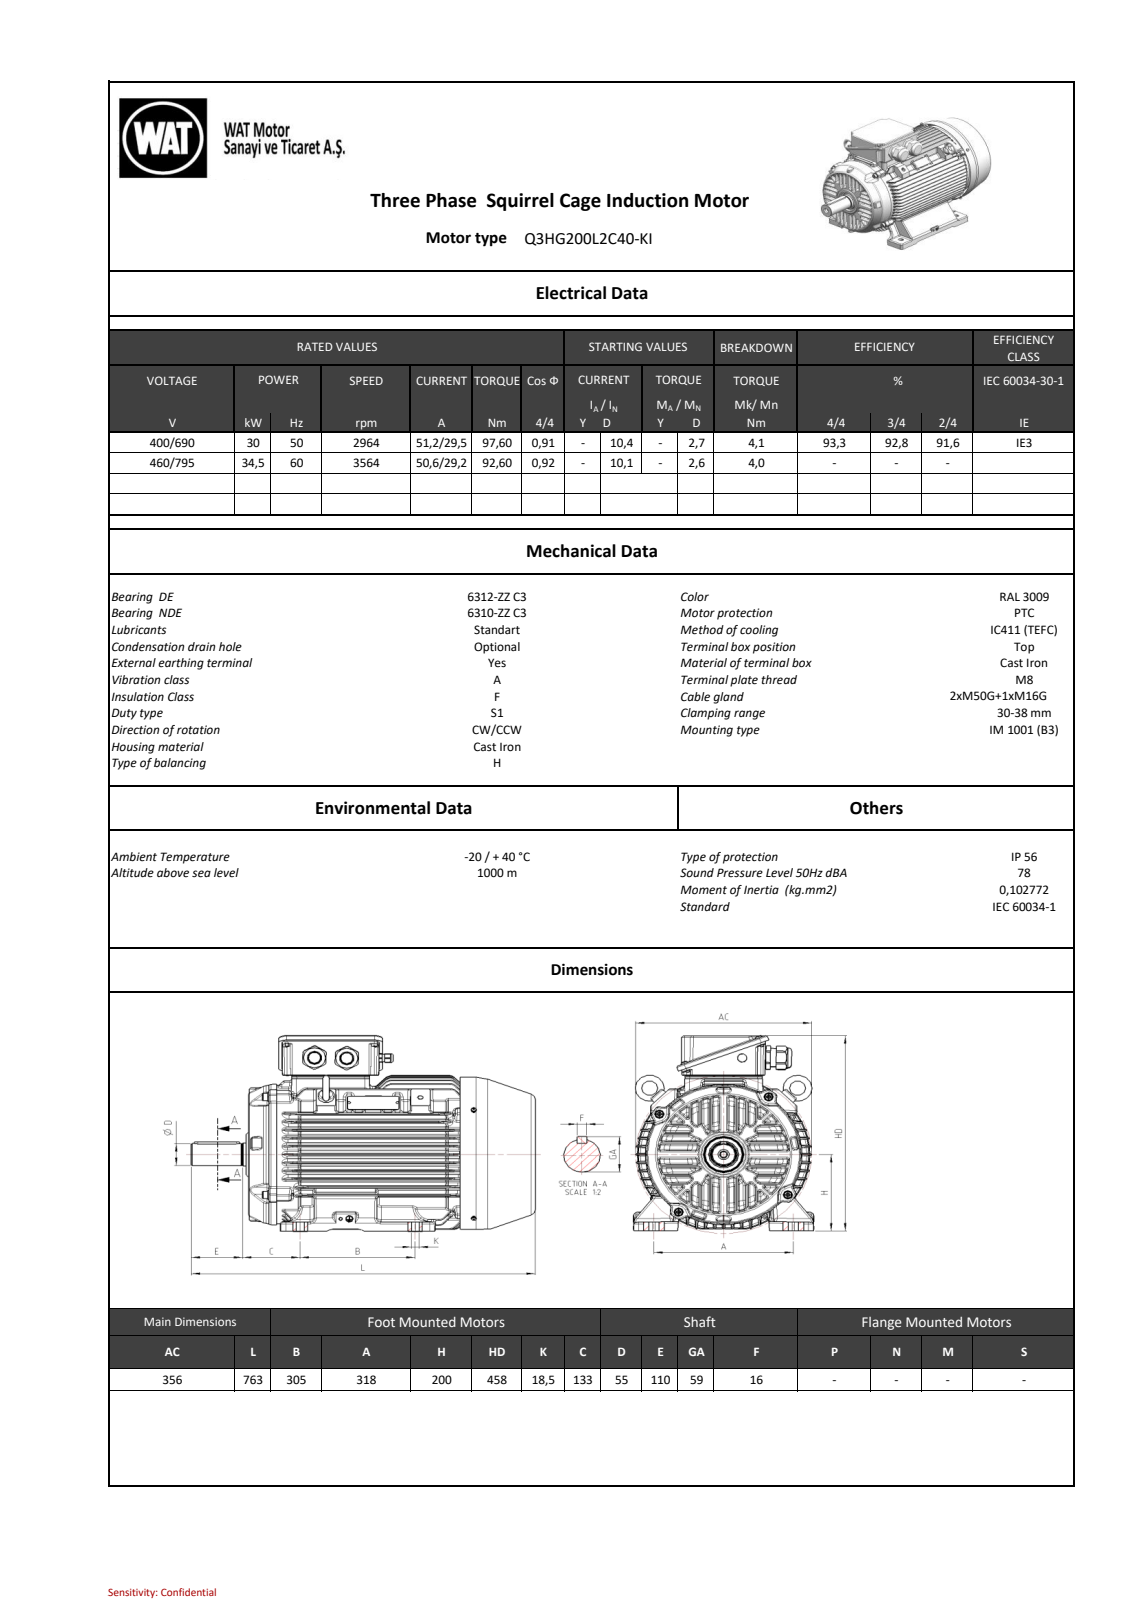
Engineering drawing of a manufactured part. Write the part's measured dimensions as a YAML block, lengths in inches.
part_name: "C9017F38B806swxd"
step_written_by: "SIEMENS PLM Software NX 11.0 (AUTOMOTIVE_DESIGN)"
units: inches
bodies: {solids: 0, faces: 7208, planar: 2145, cylindrical: 1512, other: 3551}
overall_size: [30.02, 18.021, 15.394]
round_holes:
  - {diameter: 0.406, count: 8}
  - {diameter: 0.551, count: 2}
  - {diameter: 0.098, count: 1}
  - {diameter: 0.197, count: 1}
  - {diameter: 0.248, count: 1}
  - {diameter: 0.315, count: 1}
  - {diameter: 0.689, count: 1}
  - {diameter: 0.827, count: 1}
  - {diameter: 13.528, count: 1}
round_bosses_or_shafts:
  - {diameter: 0.63, count: 8}
  - {diameter: 0.472, count: 8}
  - {diameter: 0.787, count: 3}
  - {diameter: 2.283, count: 2}
  - {diameter: 2.157, count: 2}
  - {diameter: 1.378, count: 2}
  - {diameter: 13.622, count: 1}
  - {diameter: 12.205, count: 1}
partial_cylinders:
  - {radius: 0.157, count: 385}
  - {radius: 0.118, count: 182}
  - {radius: 0.059, count: 136}
  - {radius: 0.079, count: 103}
  - {radius: 0.197, count: 49}
  - {radius: 0.071, count: 48}
  - {radius: 0.016, count: 32}
  - {radius: 0.394, count: 14}
face_to_face_distances: [0.572, 0.569, 1.142, 1.147, 0.575, 1.717, 2.311, 1.724, 1.152, 0.577]
hole_center_spacings: [6.221, 8.797, 2.16, 7.136, 10.191, 12.252, 12.441, 6.201]
